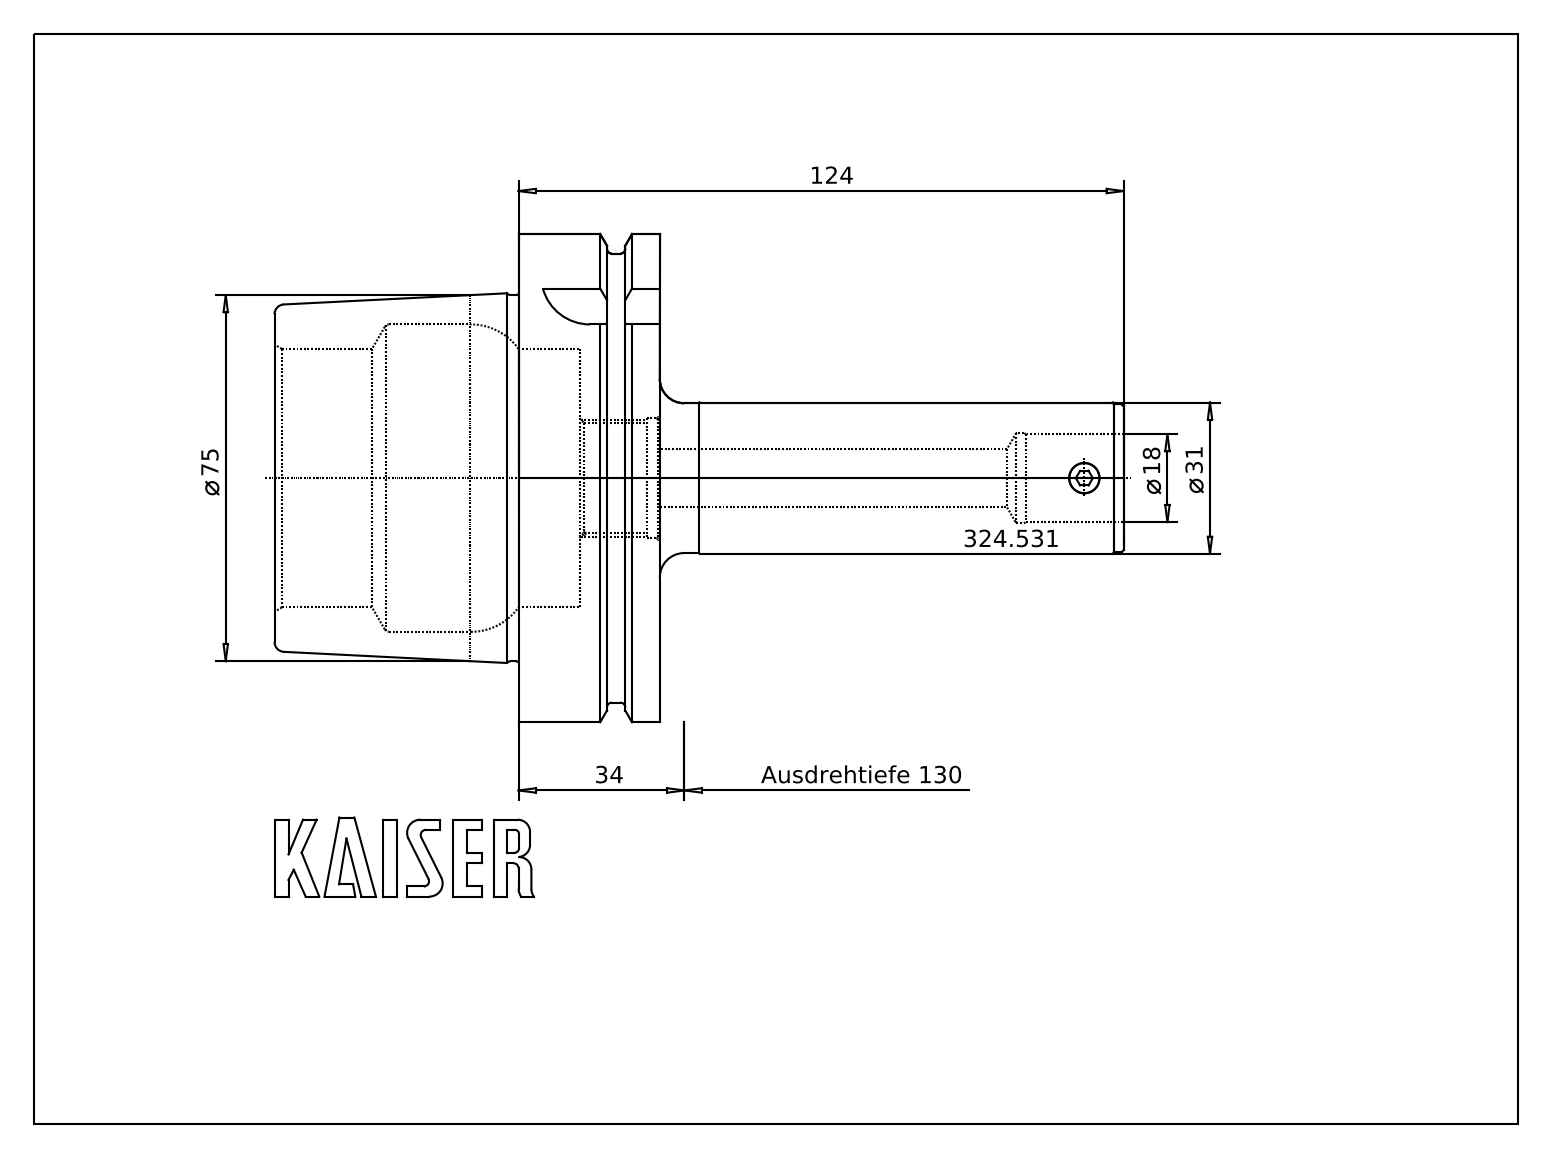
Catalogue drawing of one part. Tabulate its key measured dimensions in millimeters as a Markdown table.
| quantity | value |
| --- | --- |
| part name | 324.531 Kaiser HSK-A100xCK3x130\|690.433 Kaiser ETL M6 X 8,5 CK3;Schnitt-Linear austragen2; 324.531 Kaiser HSK-A100xCK3x130\|324.531 Kaiser HSK-A100xCK3x130;Schnitt-Rotation3 |
| STEP written by | ACIS (automotive_design) |
| units | millimeters |
| bodies | 2 solids, 273 faces (76 planar, 60 cylindrical, 137 other) |
| overall size | 173.9 × 99.93 × 99.93 |
| volume | 310 553 mm³ |
| surface area | 62 452 mm² |
| round holes (diameter × count) | 12 × 2, 5.38 × 1, 6.2 × 1, 10.06 × 1, 18 × 1, 18.5 × 1, 22.5 × 1, 24.5 × 1, 53.06 × 1, 63.14 × 1 |
| round bosses / shafts (diameter × count) | 99.93 × 1, 91.95 × 1, 31 × 1, 30.7 × 1, 30.3 × 1, 6 × 1 |
| partial cylindrical surfaces (radius × count) | 1.9 × 6, 10 × 5, 4.88 × 4, 2.75 × 2 |
| main face-to-face distances | 28.95, 16.5, 12.45, 78.85, 62.35, 49.9, 87.8, 15.85, 95.05, 111.55 |
| hole center spacings | 108.95 |
